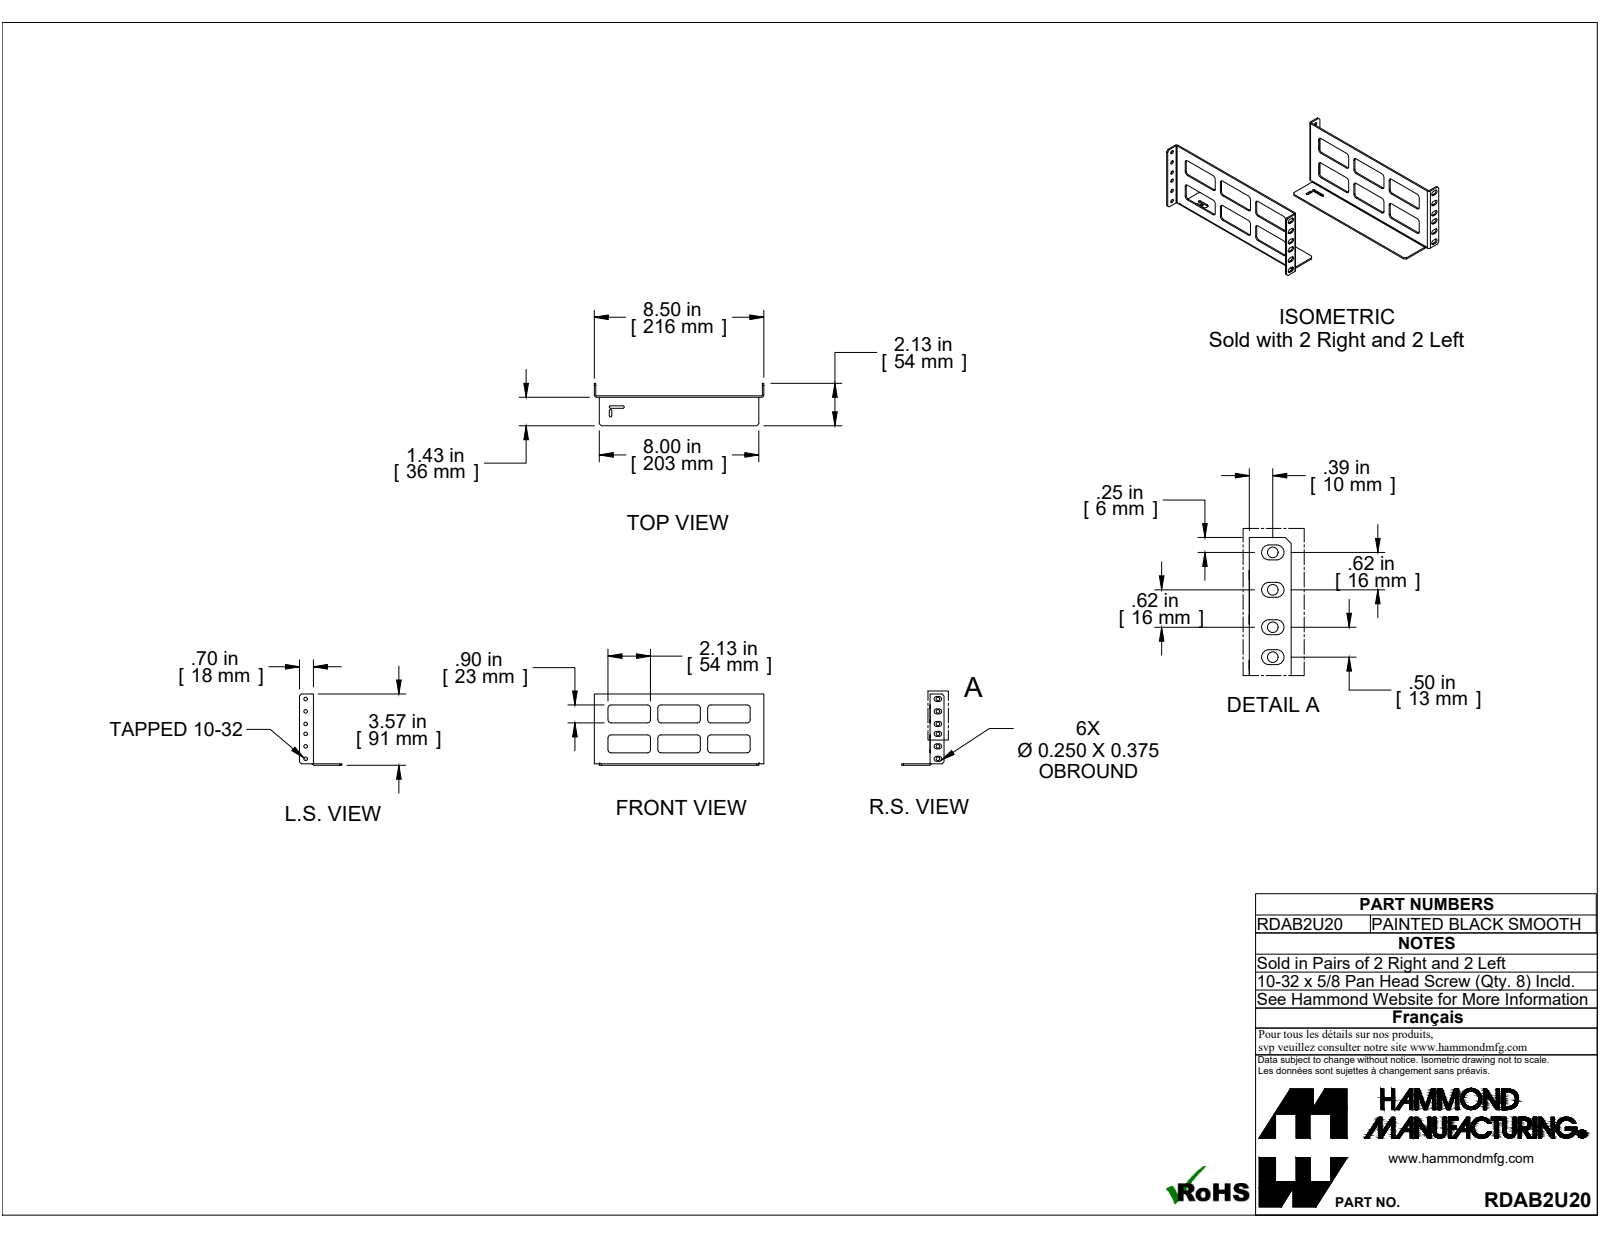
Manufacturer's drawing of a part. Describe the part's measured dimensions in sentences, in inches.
The part is named "RDAB2U20". Its 3-D file was written by "SolidWorks 2019 (CONFIG_CONTROL_DESIGN)". It is 4 solids with 476 faces: 264 planar, 212 cylindrical and 0 other. Overall it measures 20 by 18.928 by 3.572 inches. Its volume is 9.645 cubic inches and its surface area 289.8 square inches. Round holes: 13 of diameter 0.177. Partial cylindrical surfaces (rounded edges, fillets, slot ends): 48 of radius 0.157, 26 of radius 0.125, 12 of radius 0.062, 10 of radius 0.036, 10 of radius 0.108, 2 of radius 0.063, 2 of radius 0.156. The main face-to-face distances are 0.072, 17.6, 17.672, 17.528, 11.5, 8.428, 19.928, 11.572, 8.356, 8.5. The hole center spacings are 18.323, 18.312, 18.396, 1.75, 0.625, 0.625, 18.347, 1.25.
